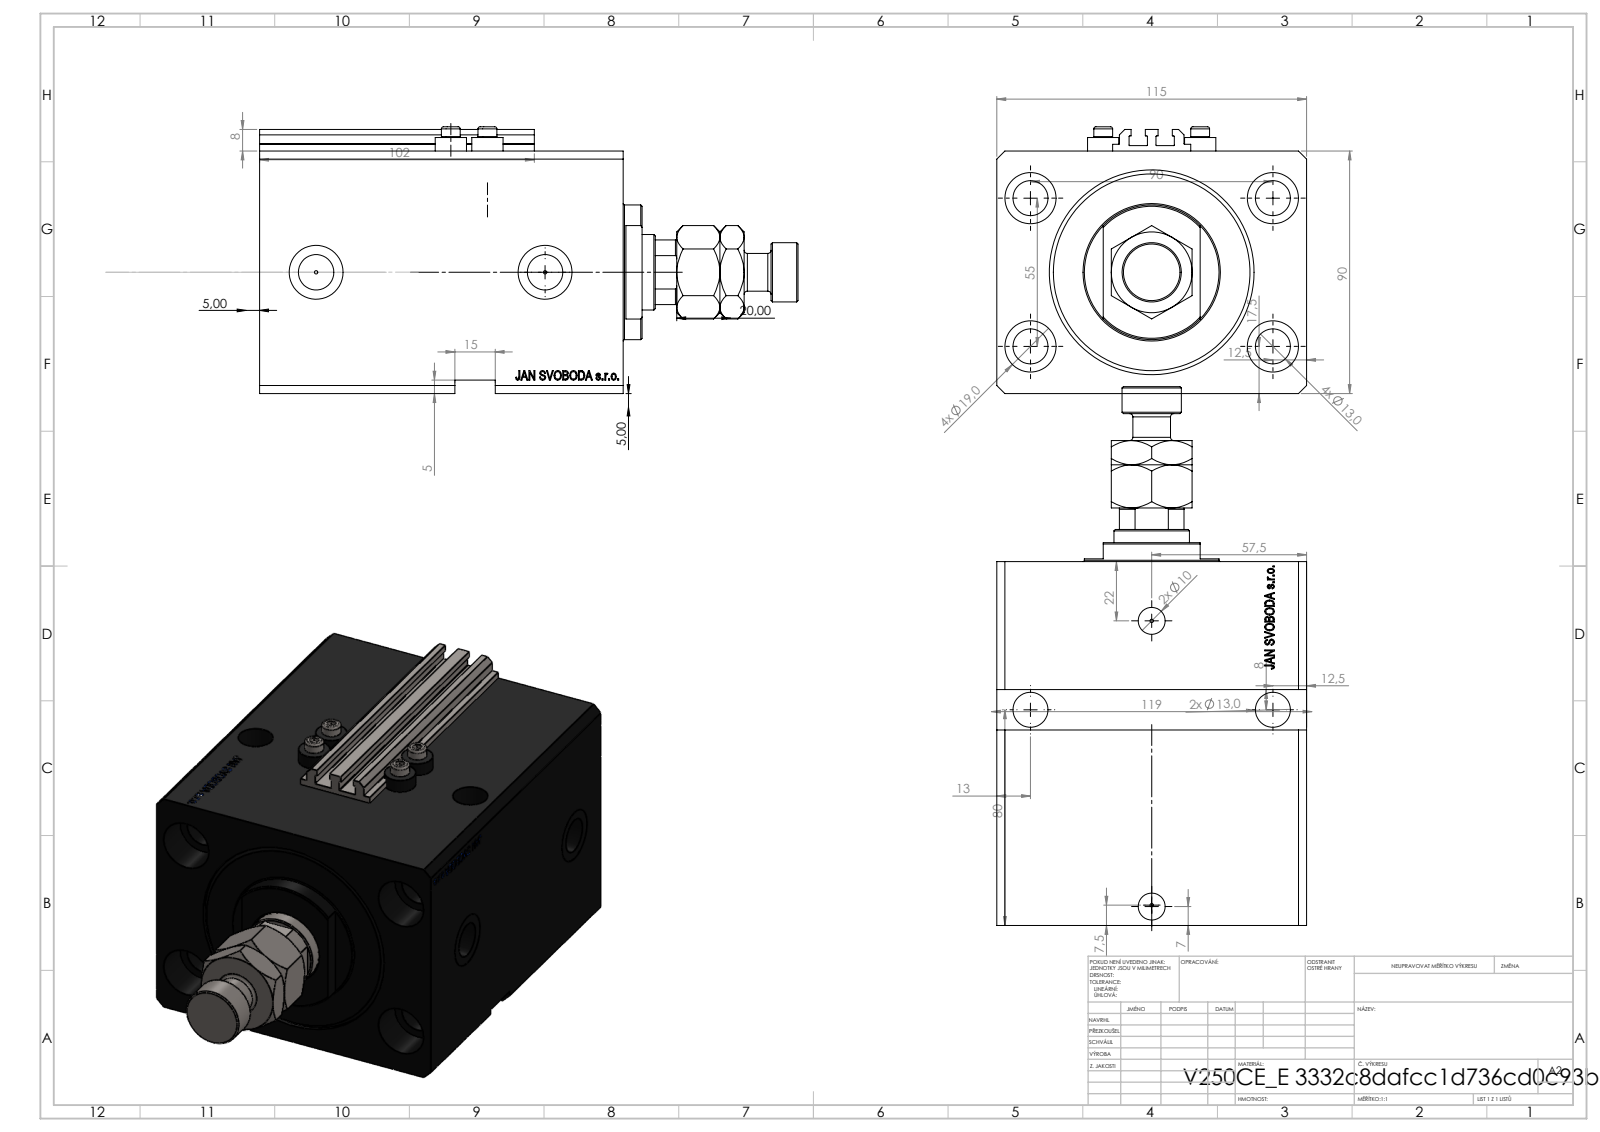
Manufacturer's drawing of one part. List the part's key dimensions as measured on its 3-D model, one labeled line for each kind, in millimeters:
Part name (STEP PRODUCT): MFA; ALLEN BOLT V250CE; V250CE_E_Body; V250CE_C_VCP (+1 more)
STEP written by: SolidWorks 2019 (CONFIG_CONTROL_DESIGN)
Units: millimetres
Bodies: 9 solids, 1195 faces (563 planar, 162 cylindrical, 470 other)
Overall size (bounding box): 200 × 115 × 99
Volume: 1 180 000 mm³ · Surface area: 193 430 mm²
Round holes (diameter × count): ⌀13 ×8, ⌀1.25 ×4, ⌀4 ×4, ⌀19 ×4, ⌀10 ×2, ⌀13.16 ×2, ⌀20 ×2, ⌀18.5 ×1, ⌀28 ×1, ⌀63 ×1, ⌀76 ×1
Round bosses / shafts (diameter × count): ⌀11.6 ×4, ⌀7 ×4, ⌀50 ×1, ⌀22 ×1, ⌀14 ×1
Partial cylindrical surfaces — rounded edges, fillets, slot ends (radius × count): R0.2 ×10, R13.5 ×1
Main face-to-face distances: 115, 90, 20, 135, 17.9, 117.1, 97.1, 65, 13, 47.1
Hole centre spacings: 52.74, 55.8, 85.76, 90, 13.6, 27.39, 28.46, 33.62
